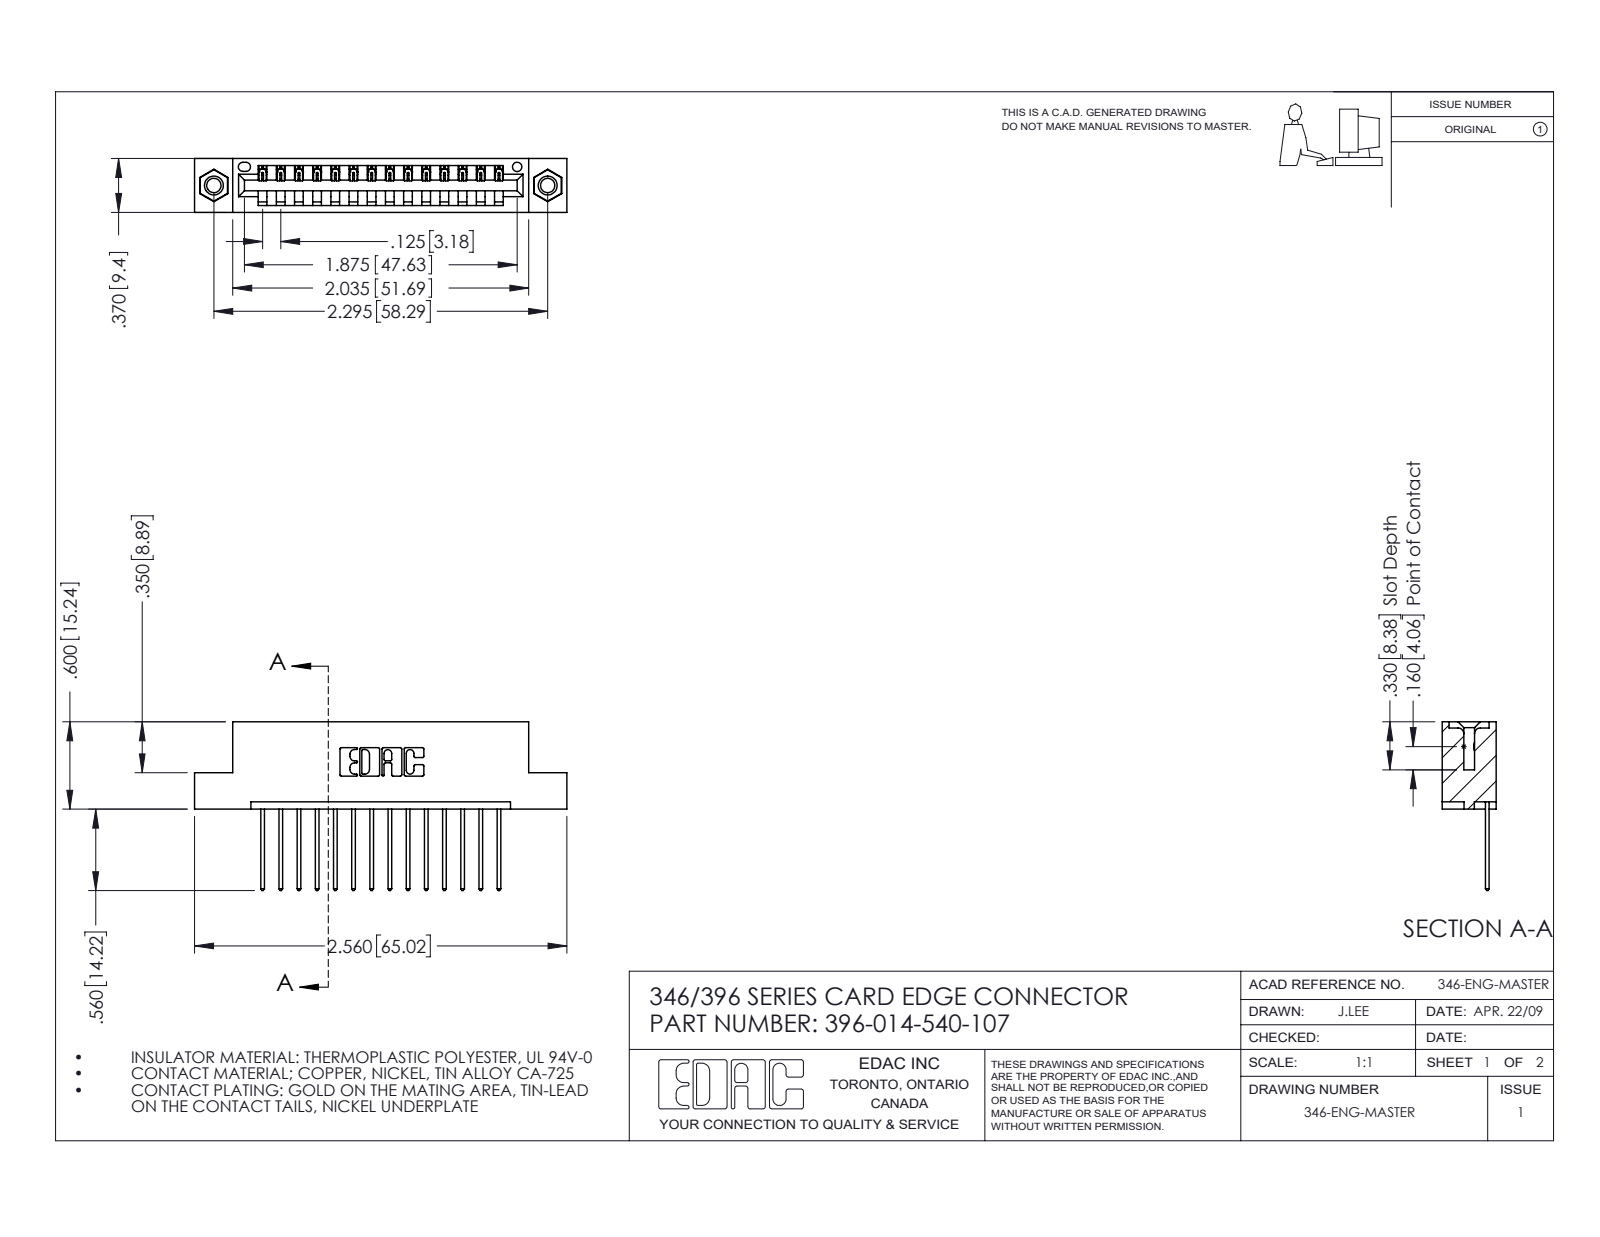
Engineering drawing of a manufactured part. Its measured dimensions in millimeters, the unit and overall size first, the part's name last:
Units: millimetres
Overall size (bounding box): 65 × 29.5 × 9.4
Round holes (diameter × count): ⌀2.5 ×2, ⌀3.2 ×2, ⌀4 ×2, ⌀1.6 ×1
Round bosses / shafts (diameter × count): ⌀3.9 ×2
Partial cylindrical surfaces — rounded edges, fillets, slot ends (radius × count): R0.2 ×28, R0.3 ×28, R0.3 ×22, R0.2 ×6, R0.8 ×6, R0.7 ×3, R0.8 ×2, R1 ×2
Main face-to-face distances: 1.2, 8.2, 6.4, 9.4, 1.8, 7.6, 0.6, 3.8, 5.6, 2.5
Hole centre spacings: 6.2, 53.1, 58.3
Volume: 6 030 mm³ · Surface area: 7 413 mm²
Bodies: 17 solids, 994 faces (668 planar, 310 cylindrical, 16 other)
Part name (STEP PRODUCT): 346 Part_Flush Mounting Lugs - 0.156 Dia-TI; 396-014-540-107; 345-292-001_345-293-140; 345-250-001_345-250-005-103
STEP written by: SolidWorks 2016 (CONFIG_CONTROL_DESIGN)
